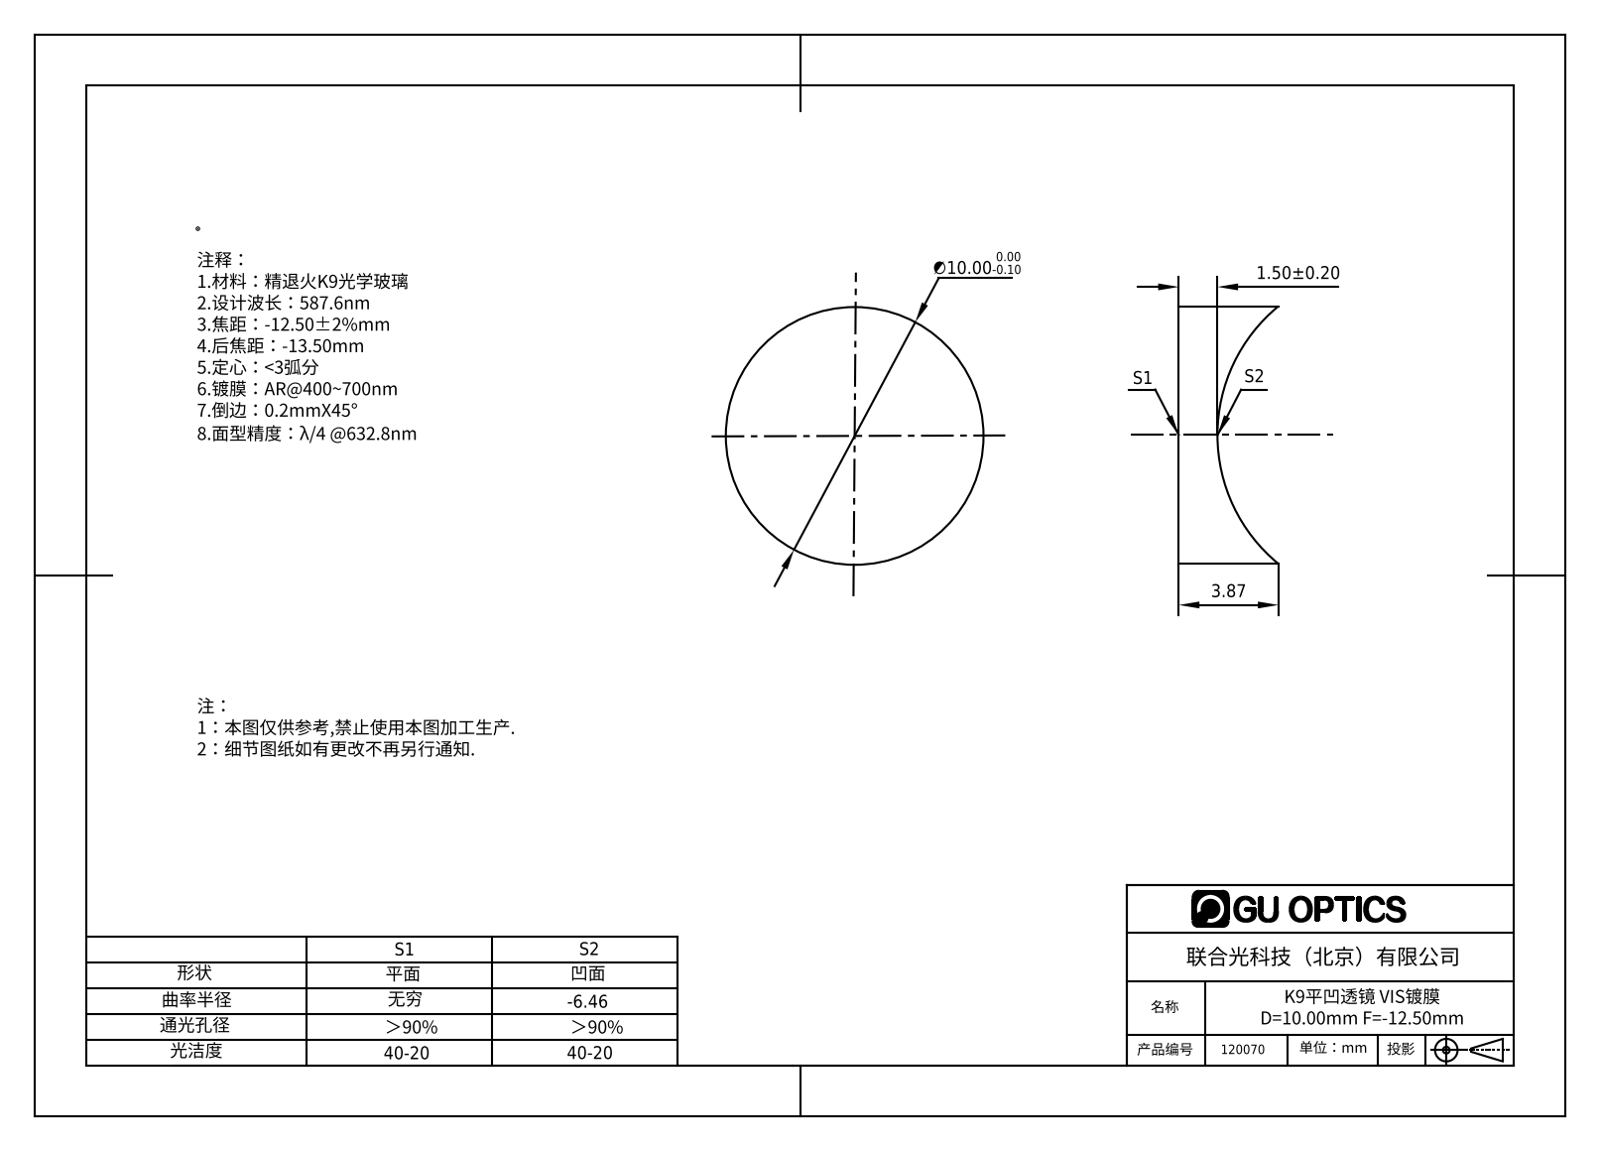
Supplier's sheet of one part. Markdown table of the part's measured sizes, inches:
| quantity | value |
| --- | --- |
| part name | 120010 |
| STEP written by | SolidWorks 2016 (AUTOMOTIVE_DESIGN) |
| units | inches |
| bodies | 1 solid, 5 faces (1 planar, 2 cylindrical, 2 other) |
| overall size | 0.394 × 0.394 × 0.152 |
| volume | 0.012 in³ |
| surface area | 0.459 in² |
| round bosses / shafts (diameter × count) | 0.394 × 1 |
